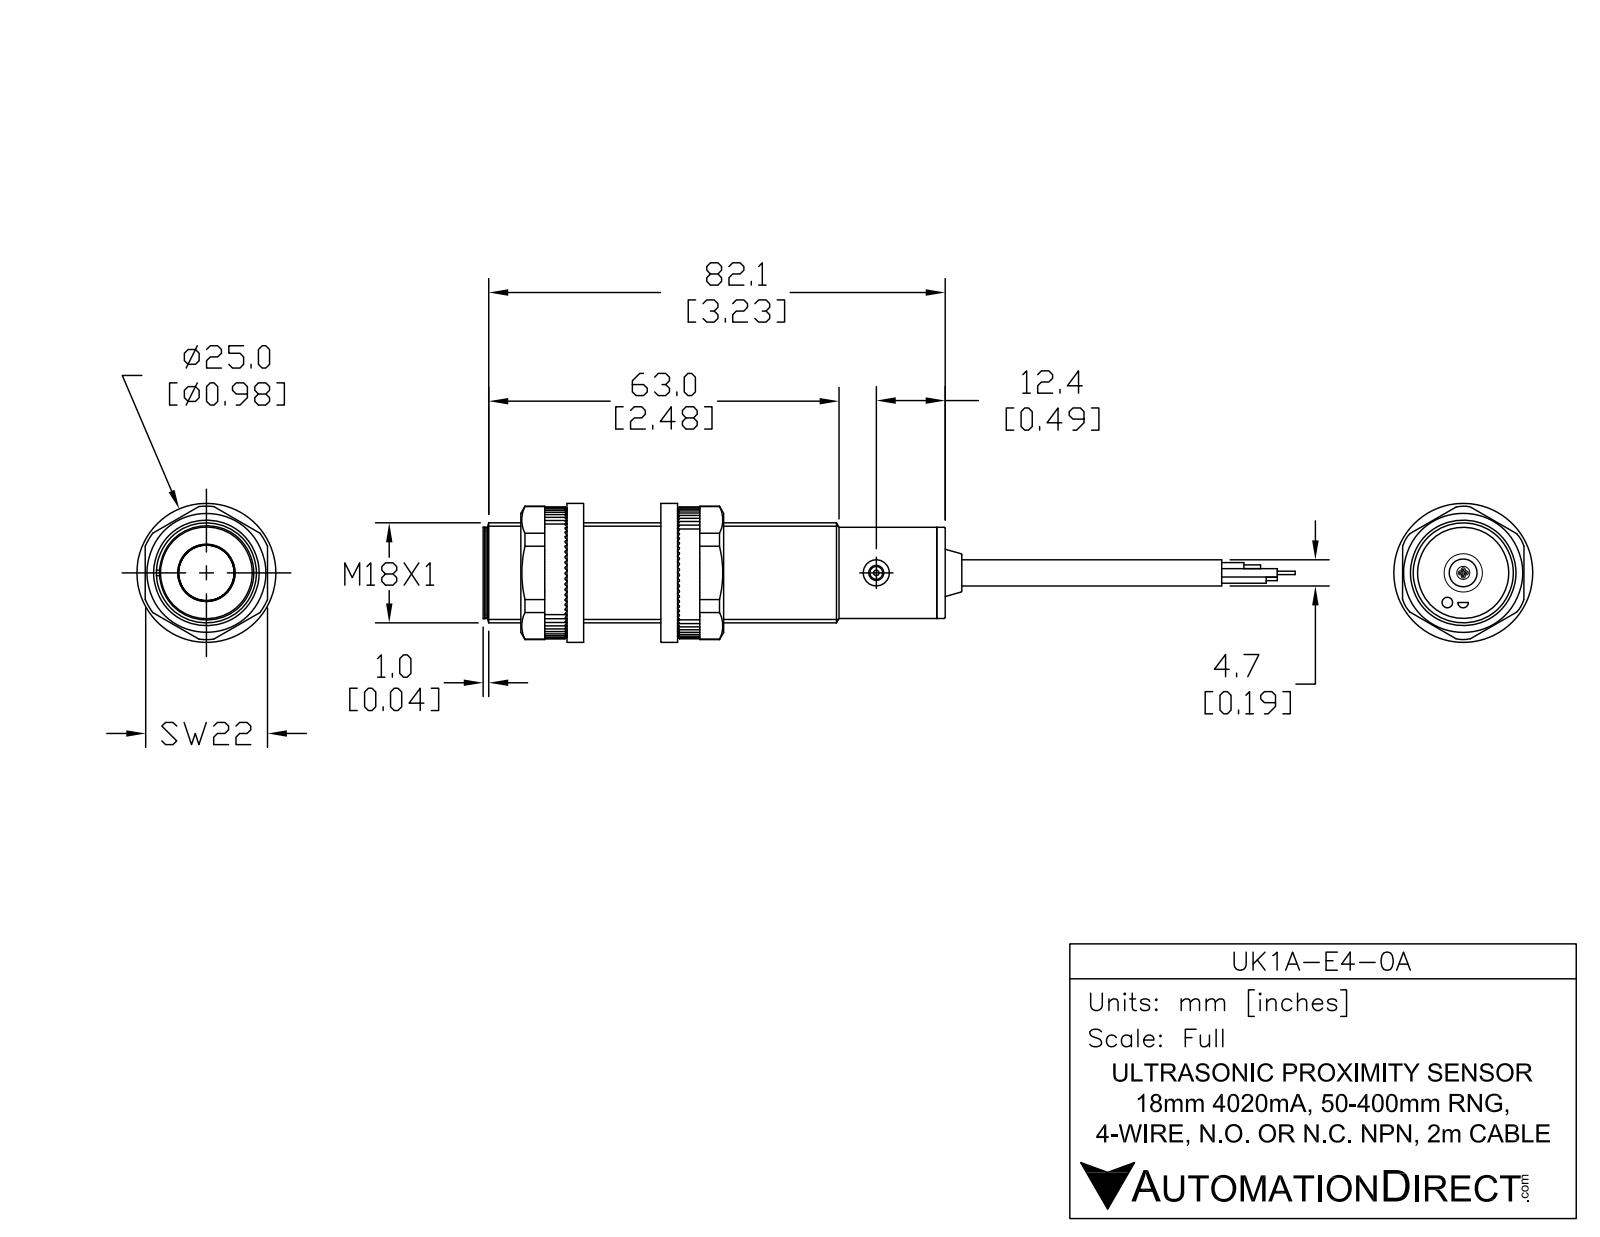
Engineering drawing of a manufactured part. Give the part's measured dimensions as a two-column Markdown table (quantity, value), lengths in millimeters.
| quantity | value |
| --- | --- |
| part name | UK1A-E4-0A |
| STEP written by | SolidWorks 2017 (AUTOMOTIVE_DESIGN) |
| units | millimeters |
| bodies | 6 solids, 55 faces (17 planar, 24 cylindrical, 14 other) |
| overall size | 122.7 × 18 × 18 |
| volume | 21 060 mm³ |
| surface area | 6 897 mm² |
| round holes (diameter × count) | 4.7 × 2, 2.7 × 1 |
| round bosses / shafts (diameter × count) | 18 × 1, 16.4 × 1, 15.8 × 1, 9.5 × 1, 4.8 × 1, 2.3 × 1 |
| main face-to-face distances | 81.1, 82.6, 1.5, 1, 82.1, 83.6, 1, 82.1, 83.6, 82.7 |
